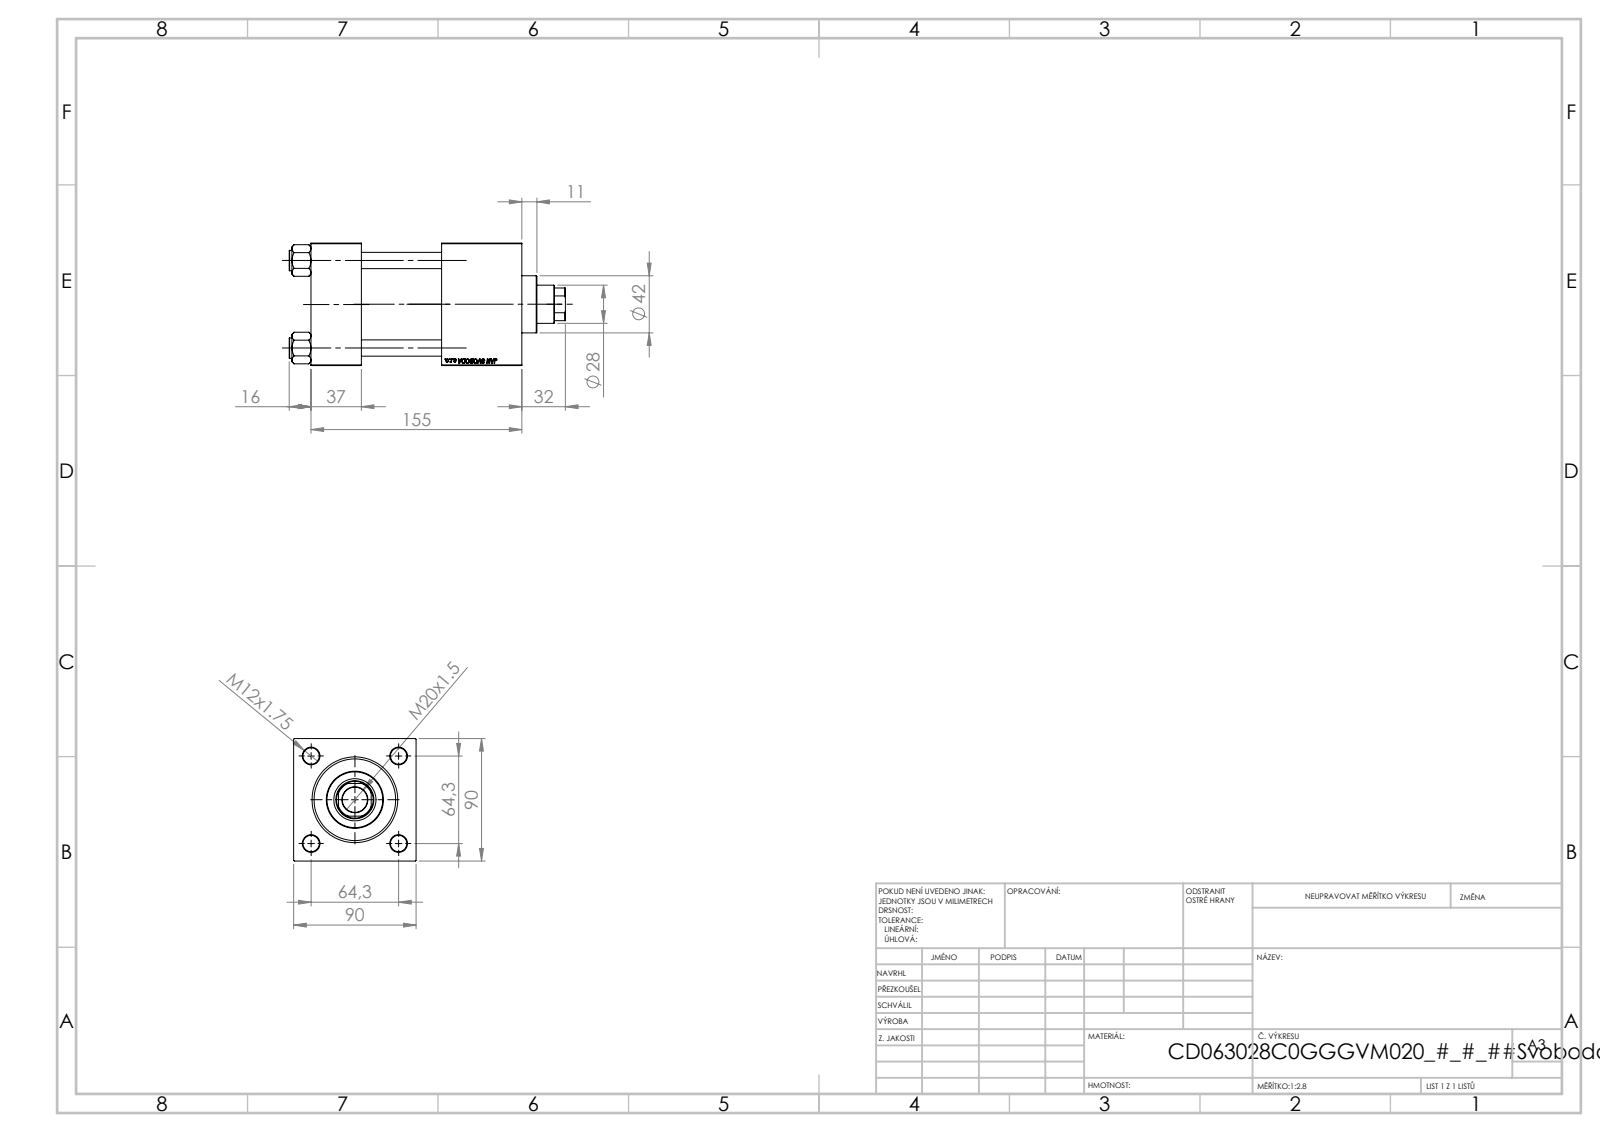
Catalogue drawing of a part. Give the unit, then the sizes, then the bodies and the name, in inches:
Units: inches
Overall size (bounding box): 7.992 × 3.543 × 3.543
Round holes (diameter × count): ⌀0.472 ×4, ⌀0.276 ×2, ⌀0.825 ×2, ⌀1.181 ×2, ⌀0.728 ×1, ⌀1.102 ×1, ⌀1.22 ×1, ⌀1.969 ×1, ⌀2.362 ×1, ⌀2.48 ×1
Round bosses / shafts (diameter × count): ⌀0.591 ×4, ⌀2.717 ×1, ⌀1.654 ×1
Partial cylindrical surfaces — rounded edges, fillets, slot ends (radius × count): R0.531 ×1
Main face-to-face distances: 3.543, 2.323, 1.457, 6.102, 4.646, 3.78, 4.972, 3.516, 1.193, 1.13
Hole centre spacings: 1.79, 2.531, 3.58, 3.839
Volume: 57.77 in³ · Surface area: 277.7 in²
Bodies: 11 solids, 1149 faces (526 planar, 87 cylindrical, 536 other)
Part name (STEP PRODUCT): V215CD_Body_C; V215CD_VC_C; V215CD_VCP_C; V215CD_C_TYCINKA (+1 more)
STEP written by: SolidWorks 2019 (CONFIG_CONTROL_DESIGN)
